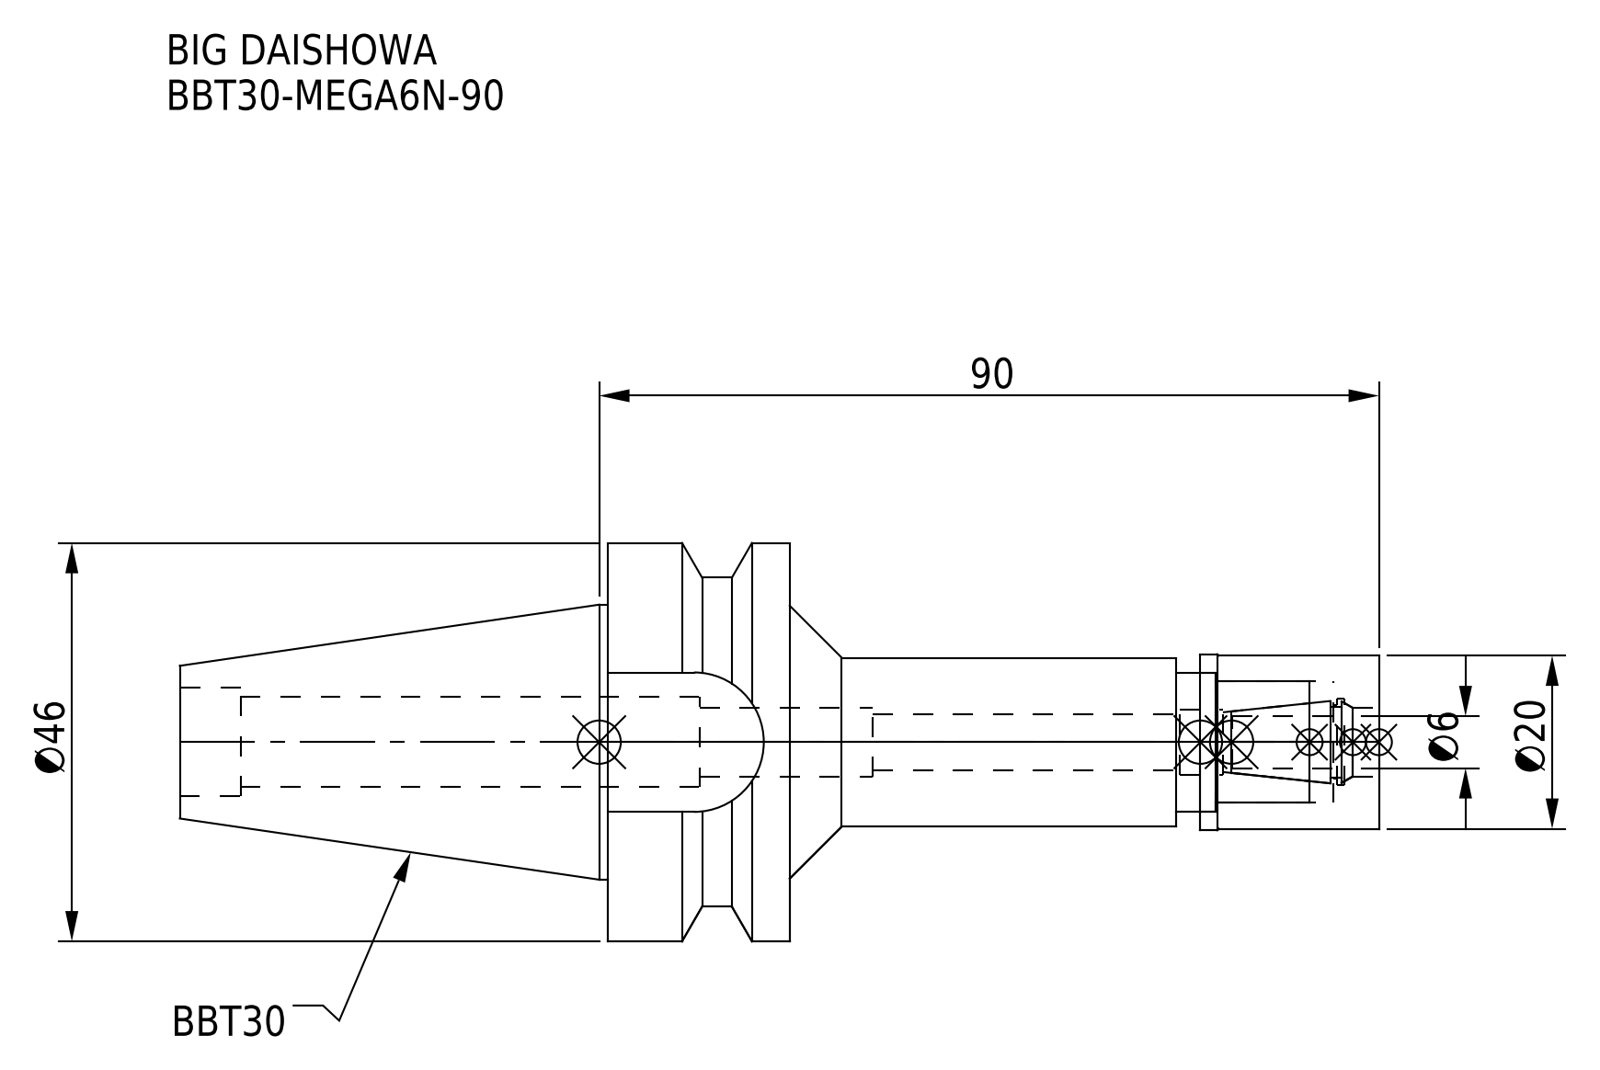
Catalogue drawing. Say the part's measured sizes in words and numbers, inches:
The part is named "MGN6_1.stp; BBT30-MEGA6N-90_1.stp; BBT30-MEGA6N-90-060.stp; DXF_TEMP_ASSY_ASM_4_ASM.stp (+3 more)". Its 3-D file was written by "SolidWorks 2019 (CONFIG_CONTROL_DESIGN)". It is 2 solids with 79 faces: 23 planar, 42 cylindrical and 14 other. Overall it measures 5.449 by 1.811 by 1.811 inches. Its volume is 4.064 cubic inches and its surface area 30.55 square inches. Round holes: 1 of diameter 0.252, 1 of diameter 0.295, 1 of diameter 0.311, 1 of diameter 0.315, 1 of diameter 0.335, 1 of diameter 0.394, 1 of diameter 0.409, 1 of diameter 0.492, 1 of diameter 0.551, 1 of diameter 0.63. Round bosses or shafts: 1 of diameter 1.811, 1 of diameter 1.25, 1 of diameter 0.799, 1 of diameter 0.787, 1 of diameter 0.768. Partial cylindrical surfaces (rounded edges, fillets, slot ends): 1 of radius 0.317, 1 of radius 0.748. The main face-to-face distances are 0.827, 2.677, 3.504, 1.283, 2.772, 2.362, 0.811, 1.866, 2.693, 5.449.
